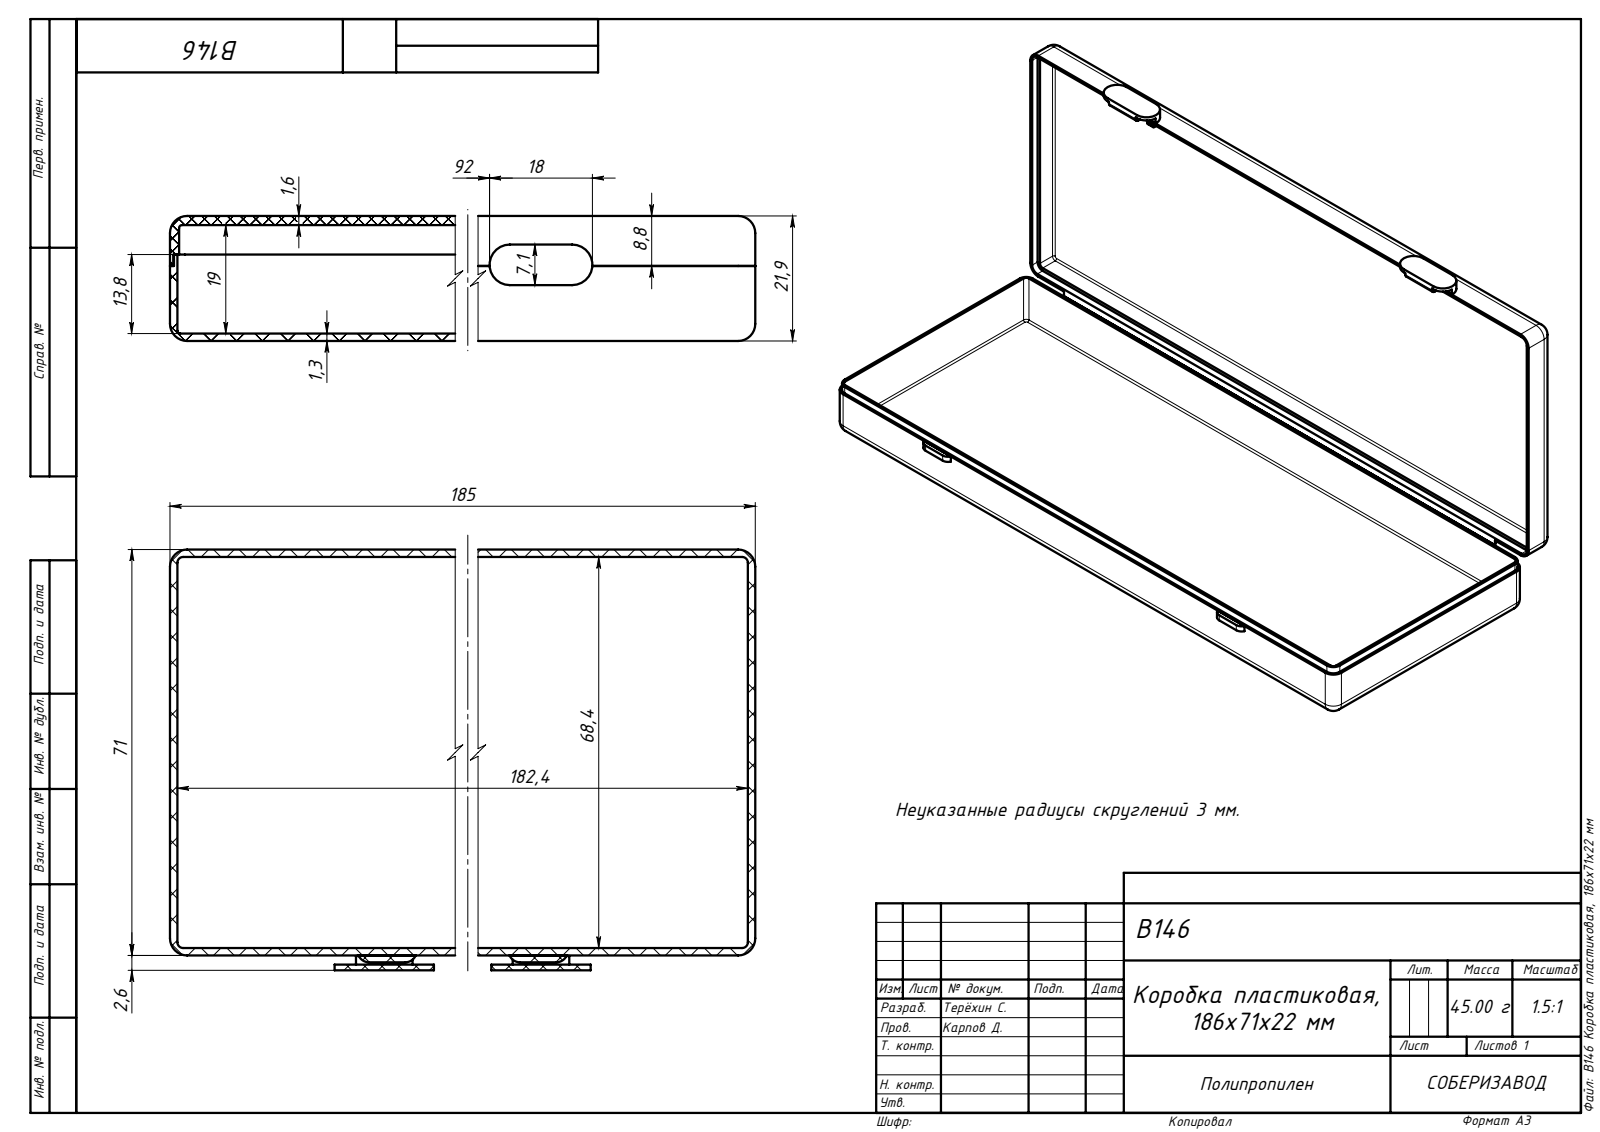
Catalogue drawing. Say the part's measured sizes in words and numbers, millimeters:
The part is named "B146 Крышка_00; B146 Емкость_00; B146 Коробка пластиковая, 186x71x22 мм". Its 3-D file was written by "SolidWorks 2019 (AUTOMOTIVE_DESIGN)". It is 8 solids with 152 faces: 78 planar, 54 cylindrical and 20 other. Overall it measures 185 by 75.1 by 21.87 millimeters. Its volume is 50 119 cubic millimeters and its surface area 75 272 square millimeters. Partial cylindrical surfaces (rounded edges, fillets, slot ends): 12 of radius 3, 9 of radius 0.5, 9 of radius 1, 5 of radius 2, 4 of radius 1.9, 4 of radius 2.4, 4 of radius 3.55. The main face-to-face distances are 1.3, 1.6, 18.97, 20.57, 20.27, 21.87, 69.7, 71, 68.4, 183.7.
